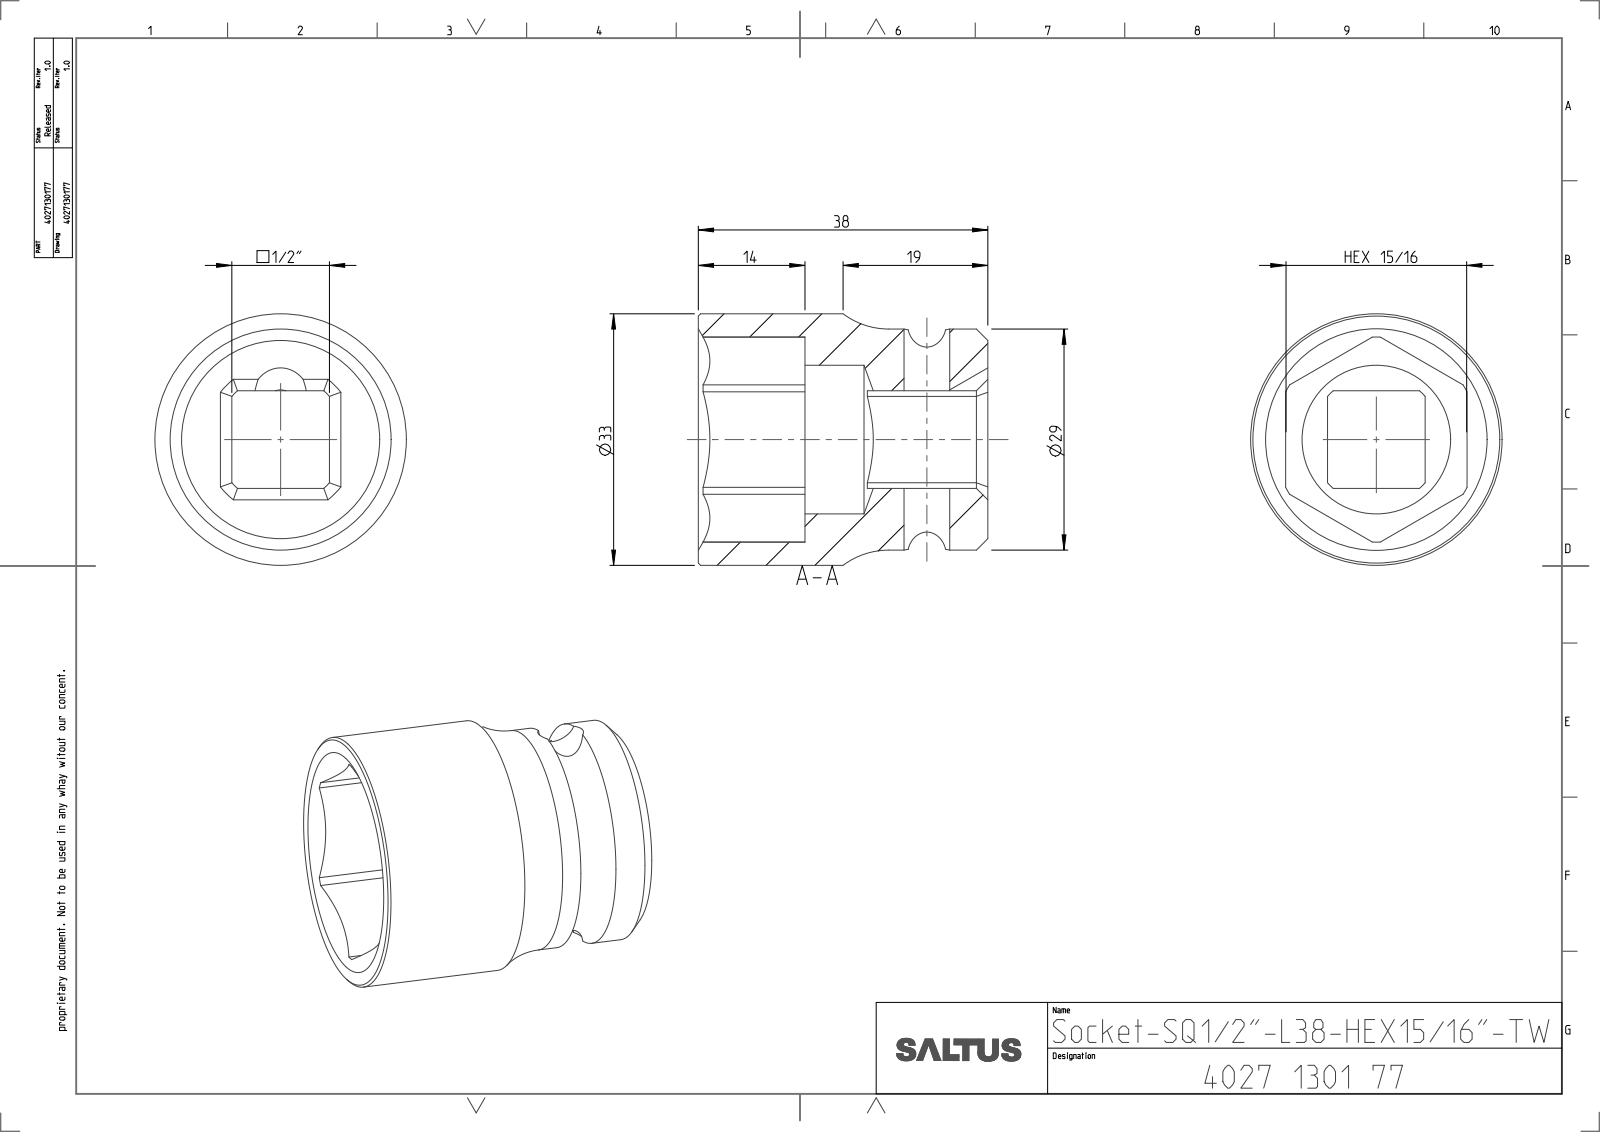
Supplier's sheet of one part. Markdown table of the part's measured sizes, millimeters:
| quantity | value |
| --- | --- |
| part name | 4027130177 |
| STEP written by | CREO PARAMETRIC BY PTC INC, 2022414 (CONFIG_CONTROL_DESIGN) |
| units | millimeters |
| bodies | 1 solid, 57 faces (18 planar, 23 cylindrical, 16 other) |
| overall size | 38 × 33 × 33 |
| volume | 15 976 mm³ |
| surface area | 7 388 mm² |
| round holes (diameter × count) | 6 × 1, 19.5 × 1 |
| round bosses / shafts (diameter × count) | 33 × 1, 29 × 1 |
| partial cylindrical surfaces (radius × count) | 4 × 1, 8.55 × 1, 13.45 × 1 |
| main face-to-face distances | 23.8, 5.49, 18.31, 12.82, 24, 38, 14 |
